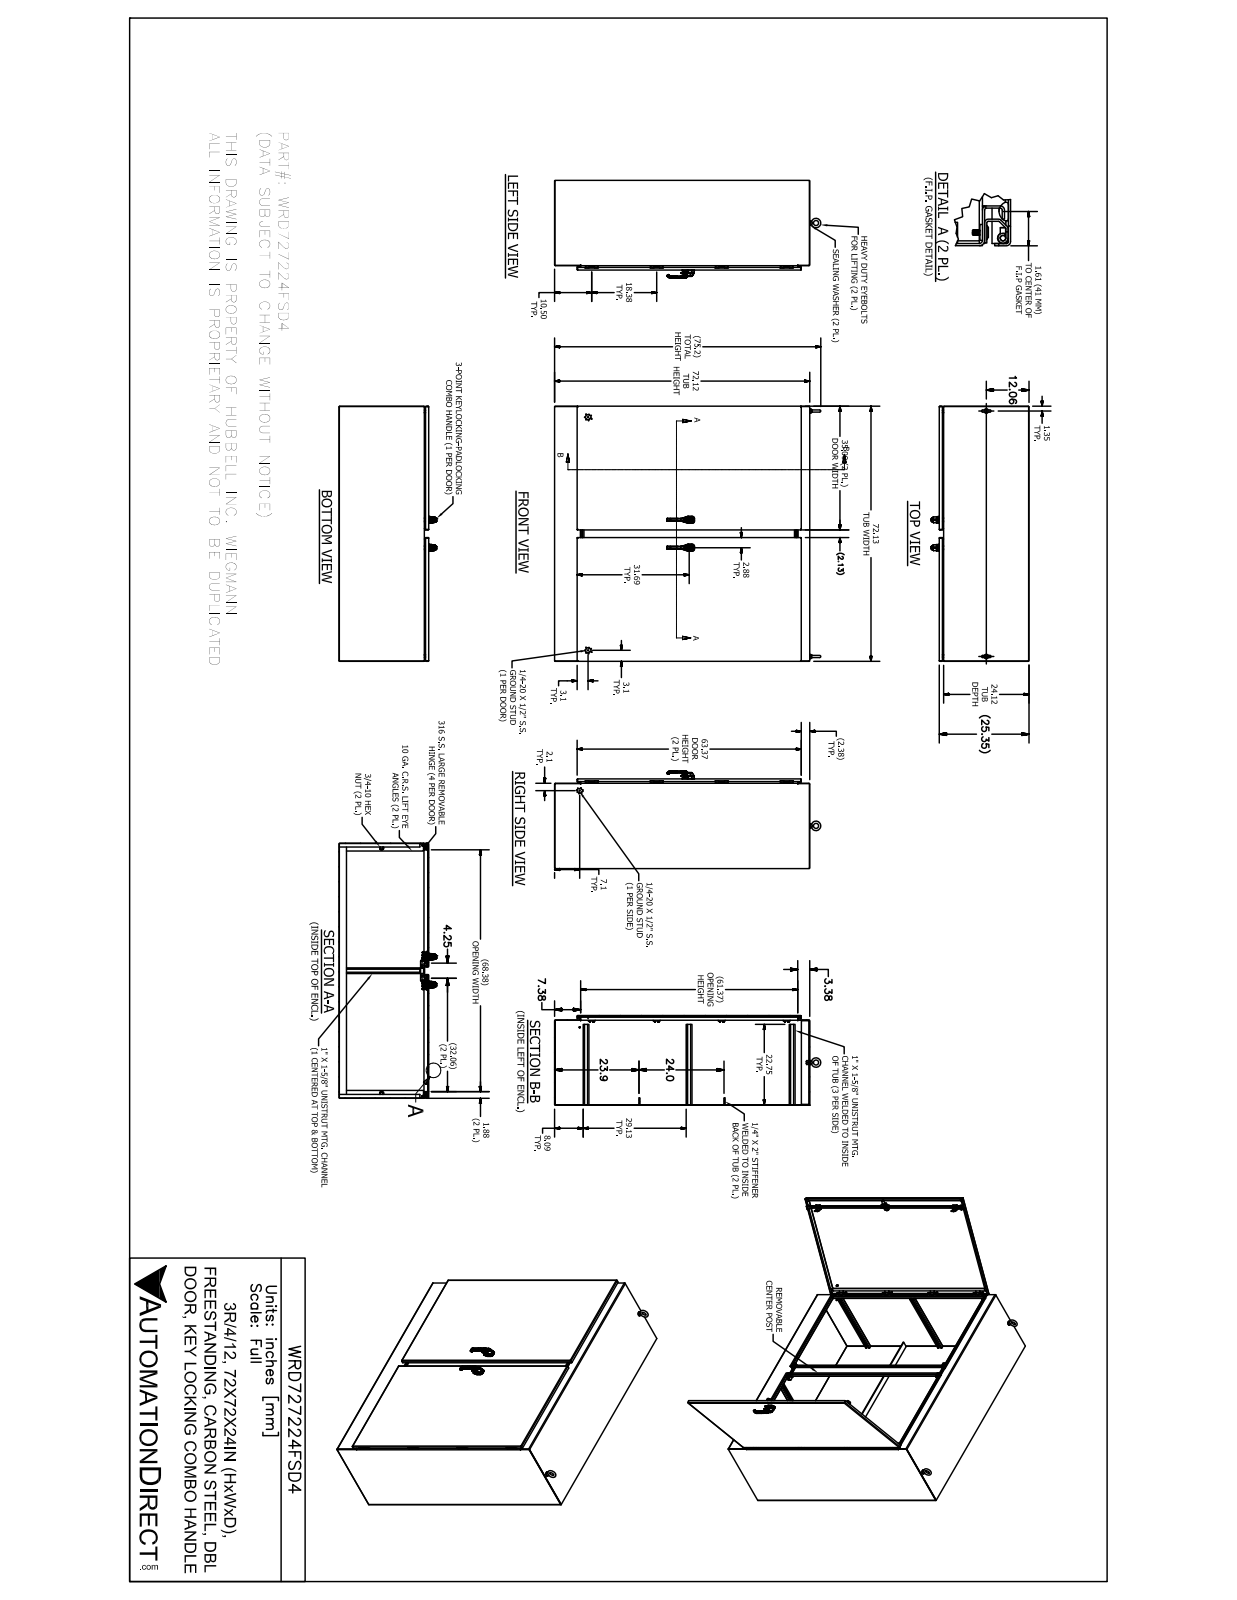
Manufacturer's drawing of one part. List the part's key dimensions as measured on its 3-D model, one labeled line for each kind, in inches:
Part name (STEP PRODUCT): WRD727224FSD4
STEP written by: SolidWorks 2017 (AUTOMOTIVE_DESIGN)
Units: inches
Bodies: 155 solids, 3276 faces (1520 planar, 1096 cylindrical, 660 other)
Overall size (bounding box): 75.248 × 72.133 × 27.527
Volume: 2 304 in³ · Surface area: 42 027 in²
Round holes (diameter × count): ⌀0.266 ×20, ⌀0.23 ×16, ⌀0.281 ×16, ⌀0.65 ×16, ⌀0.2 ×8, ⌀0.277 ×8, ⌀0.281 ×6, ⌀0.156 ×4, ⌀0.252 ×4, ⌀0.4 ×4, ⌀0.45 ×4, ⌀0.241 ×3
Round bosses / shafts (diameter × count): ⌀0.625 ×15, ⌀0.25 ×13, ⌀0.533 ×4, ⌀0.438 ×4, ⌀0.375 ×4, ⌀0.313 ×4, ⌀0.213 ×4, ⌀1 ×3
Partial cylindrical surfaces — rounded edges, fillets, slot ends (radius × count): R0.062 ×47, R0.05 ×32, R0.125 ×32, R0.01 ×16, R0.019 ×16, R0.025 ×16, R0.053 ×16, R0.067 ×16
Main face-to-face distances: 0.104, 25.245, 72.021, 25.141, 25.349, 71.917, 72.125, 24.021, 1.224, 23.917
Hole centre spacings: 1, 18.375, 36.75, 73.219, 73.218, 1.102, 1.195, 18.375
